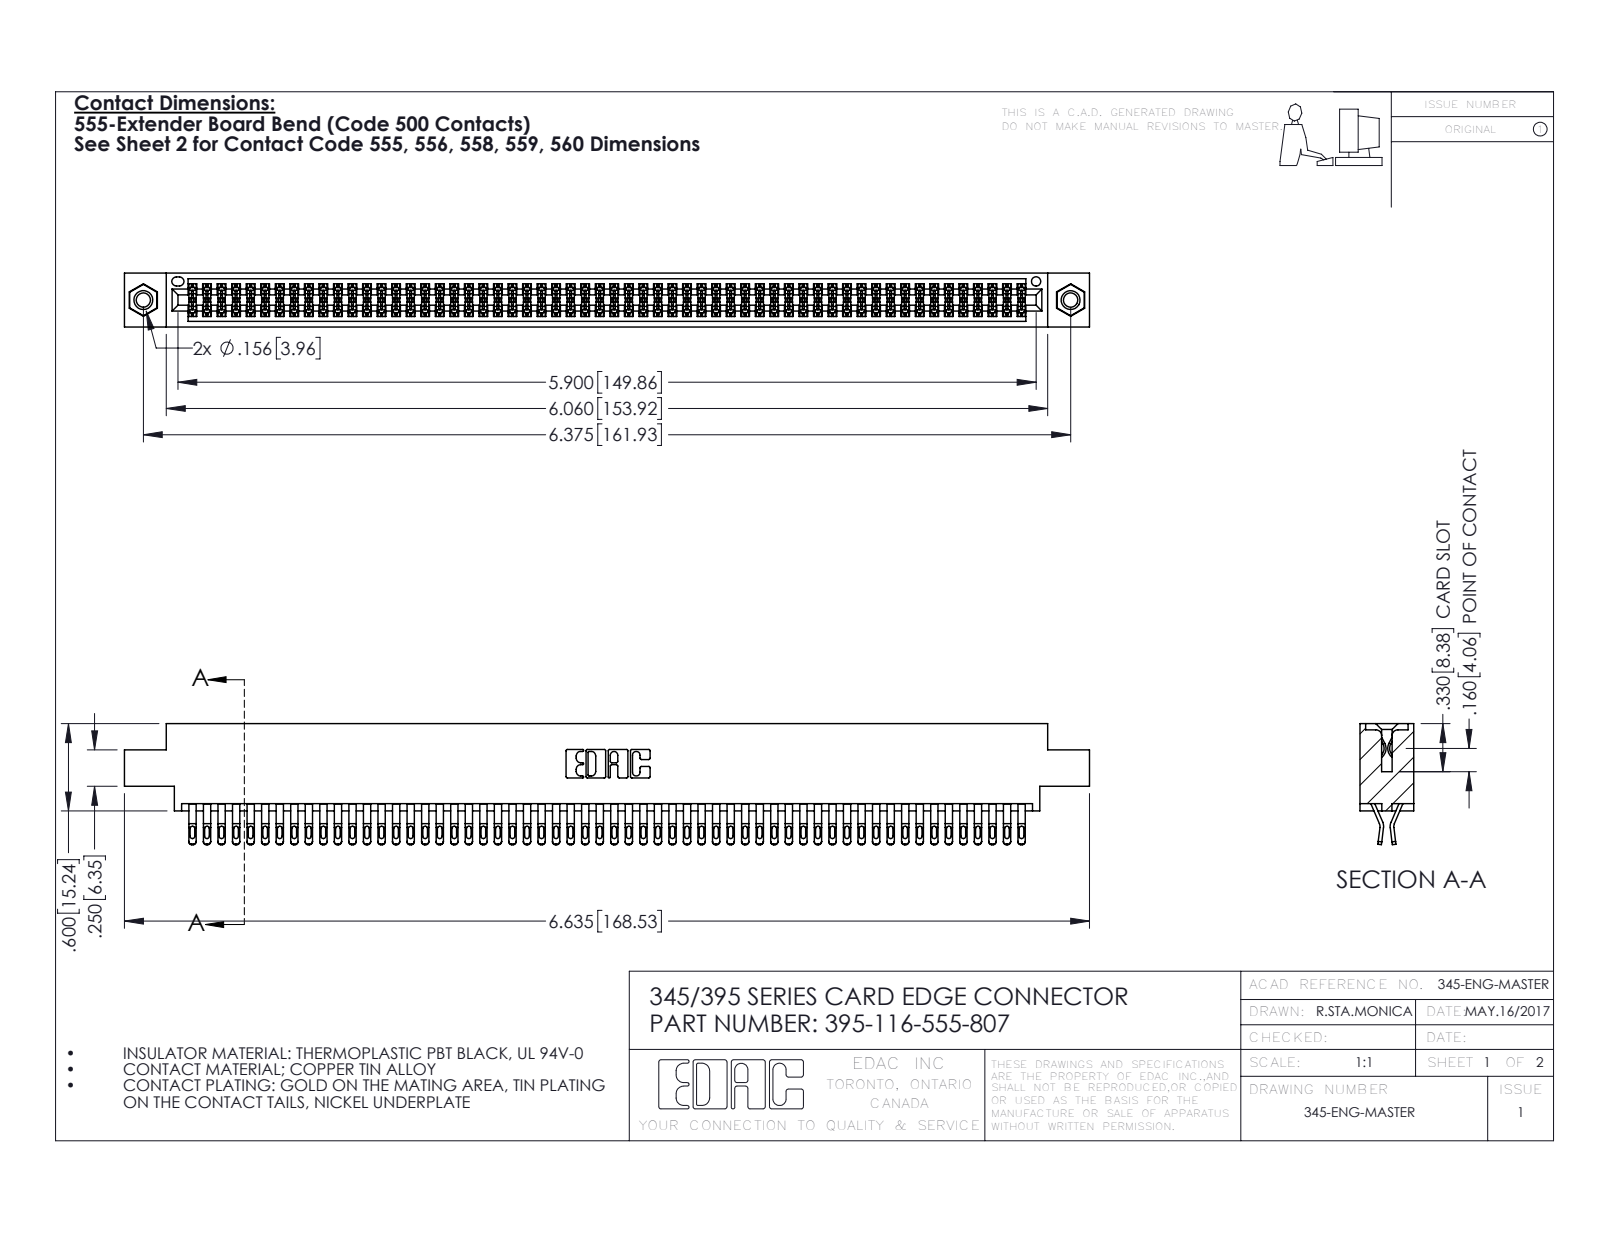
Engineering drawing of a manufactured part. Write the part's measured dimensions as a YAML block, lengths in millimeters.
part_name: "345-292-001_555 Tail; 395-116-555-807; 345-250-001_345-250-005-103; 345 Part_0.170 Offset - 0.156 Dia-TI"
step_written_by: "SolidWorks 2016 (CONFIG_CONTROL_DESIGN)"
units: millimeters
bodies: {solids: 119, faces: 6686, planar: 3712, cylindrical: 2958, other: 16}
overall_size: [168.5, 21.1, 9.4]
volume: 16730
surface_area: 26380
round_holes:
  - {diameter: 2.5, count: 2}
  - {diameter: 3.2, count: 2}
  - {diameter: 4, count: 2}
  - {diameter: 1.6, count: 1}
round_bosses_or_shafts:
  - {diameter: 3.9, count: 2}
partial_cylinders:
  - {radius: 0.4, count: 290}
  - {radius: 0.5, count: 232}
  - {radius: 0.2, count: 174}
  - {radius: 0.3, count: 22}
  - {radius: 0.2, count: 6}
  - {radius: 0.8, count: 6}
  - {radius: 0.7, count: 3}
  - {radius: 0.3, count: 2}
face_to_face_distances: [1.8, 7.6, 9.4, 0.6, 5.1, 2.5, 6.9, 5.7, 4.4, 3.8]
hole_center_spacings: [6.9, 155.9, 161.9]
